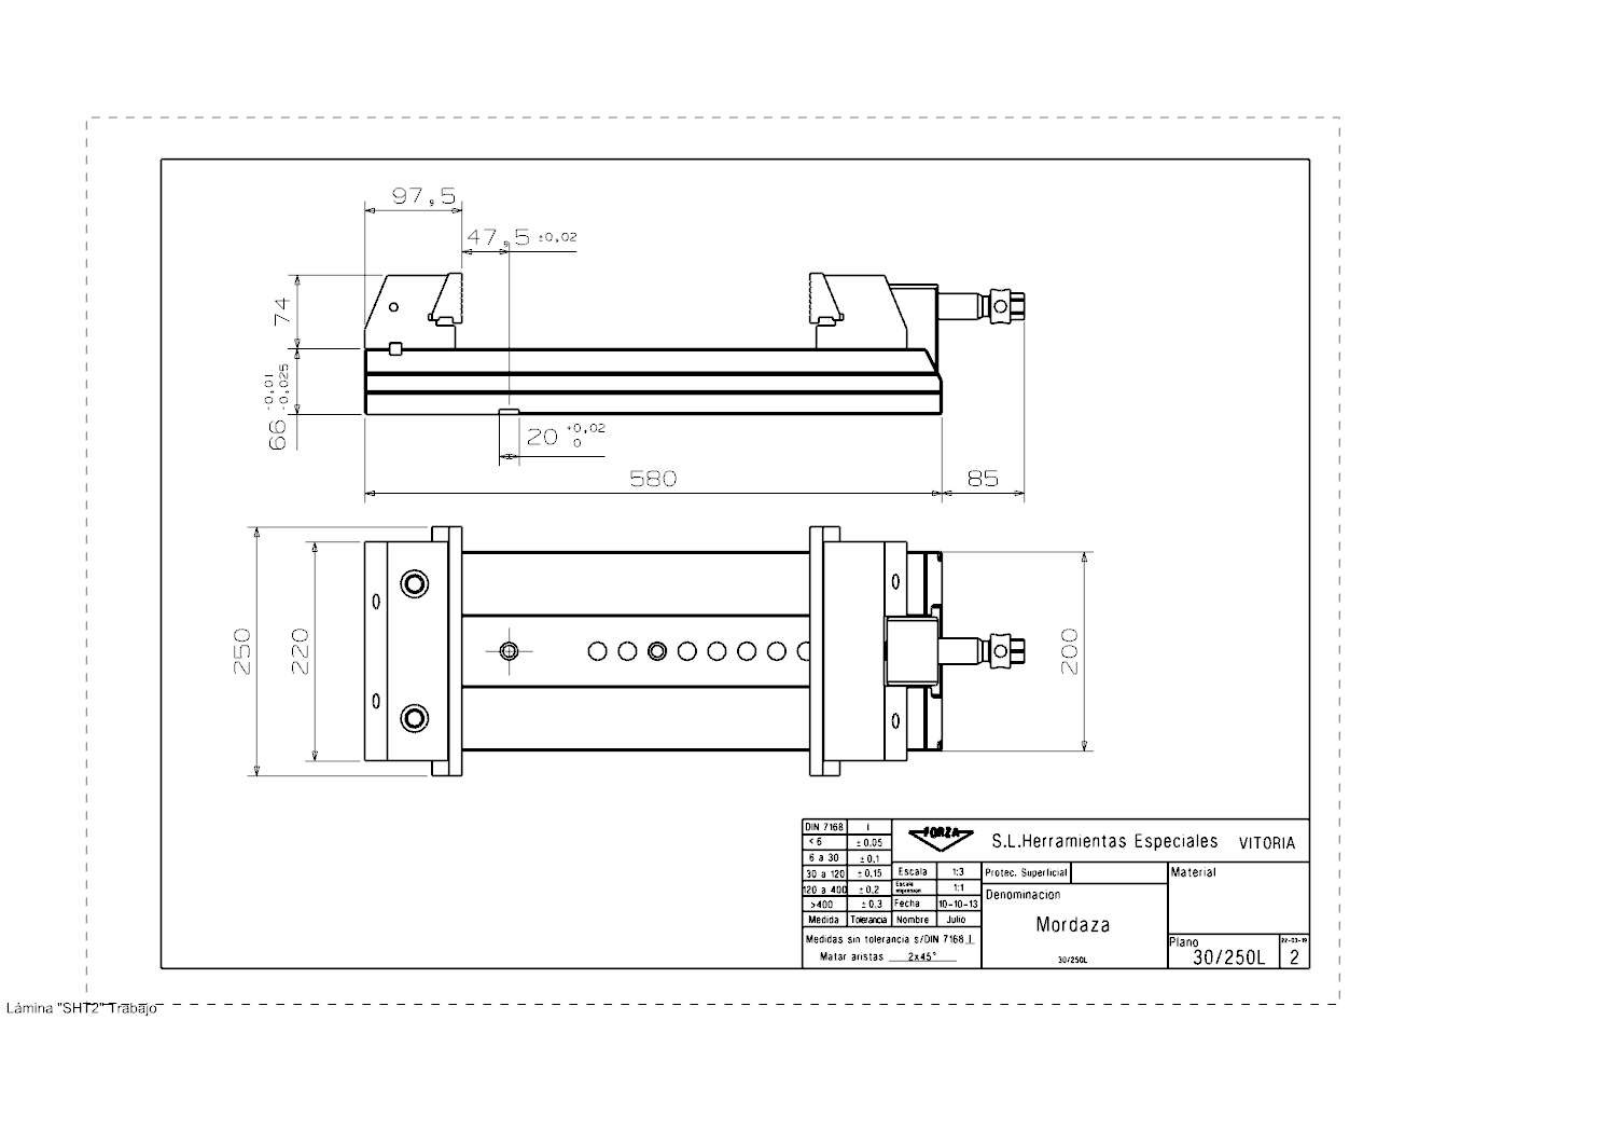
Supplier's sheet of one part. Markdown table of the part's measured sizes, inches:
| quantity | value |
| --- | --- |
| part name | 30_250L_Mordaza |
| STEP written by | SIEMENS PLM Software NX 11.0 (AUTOMOTIVE_DESIGN) |
| units | inches |
| bodies | 13 solids, 625 faces (462 planar, 103 cylindrical, 60 other) |
| overall size | 26.102 × 9.843 × 5.591 |
| volume | 544.9 in³ |
| surface area | 1 243 in² |
| round holes (diameter × count) | 0.748 × 5, 0.204 × 4, 0.374 × 4, 0.591 × 4, 0.709 × 4, 0.236 × 3, 0.346 × 3, 0.417 × 3, 0.487 × 3, 0.512 × 3, 0.256 × 2, 0.275 × 2 |
| round bosses / shafts (diameter × count) | 1.339 × 1, 1.331 × 1, 1.024 × 1, 0.787 × 1, 0.65 × 1 |
| partial cylindrical surfaces (radius × count) | 0.394 × 8, 0.256 × 2, 0.354 × 1, 0.413 × 1, 0.492 × 1, 0.522 × 1 |
| main face-to-face distances | 2.598, 1.346, 1.252, 0.059, 1.287, 2.539, 0.394, 2.559, 5.709, 2.913 |
| hole center spacings | 0.787, 0.866, 0.996, 1.075, 1.115, 1.181, 1.393, 1.824 |
